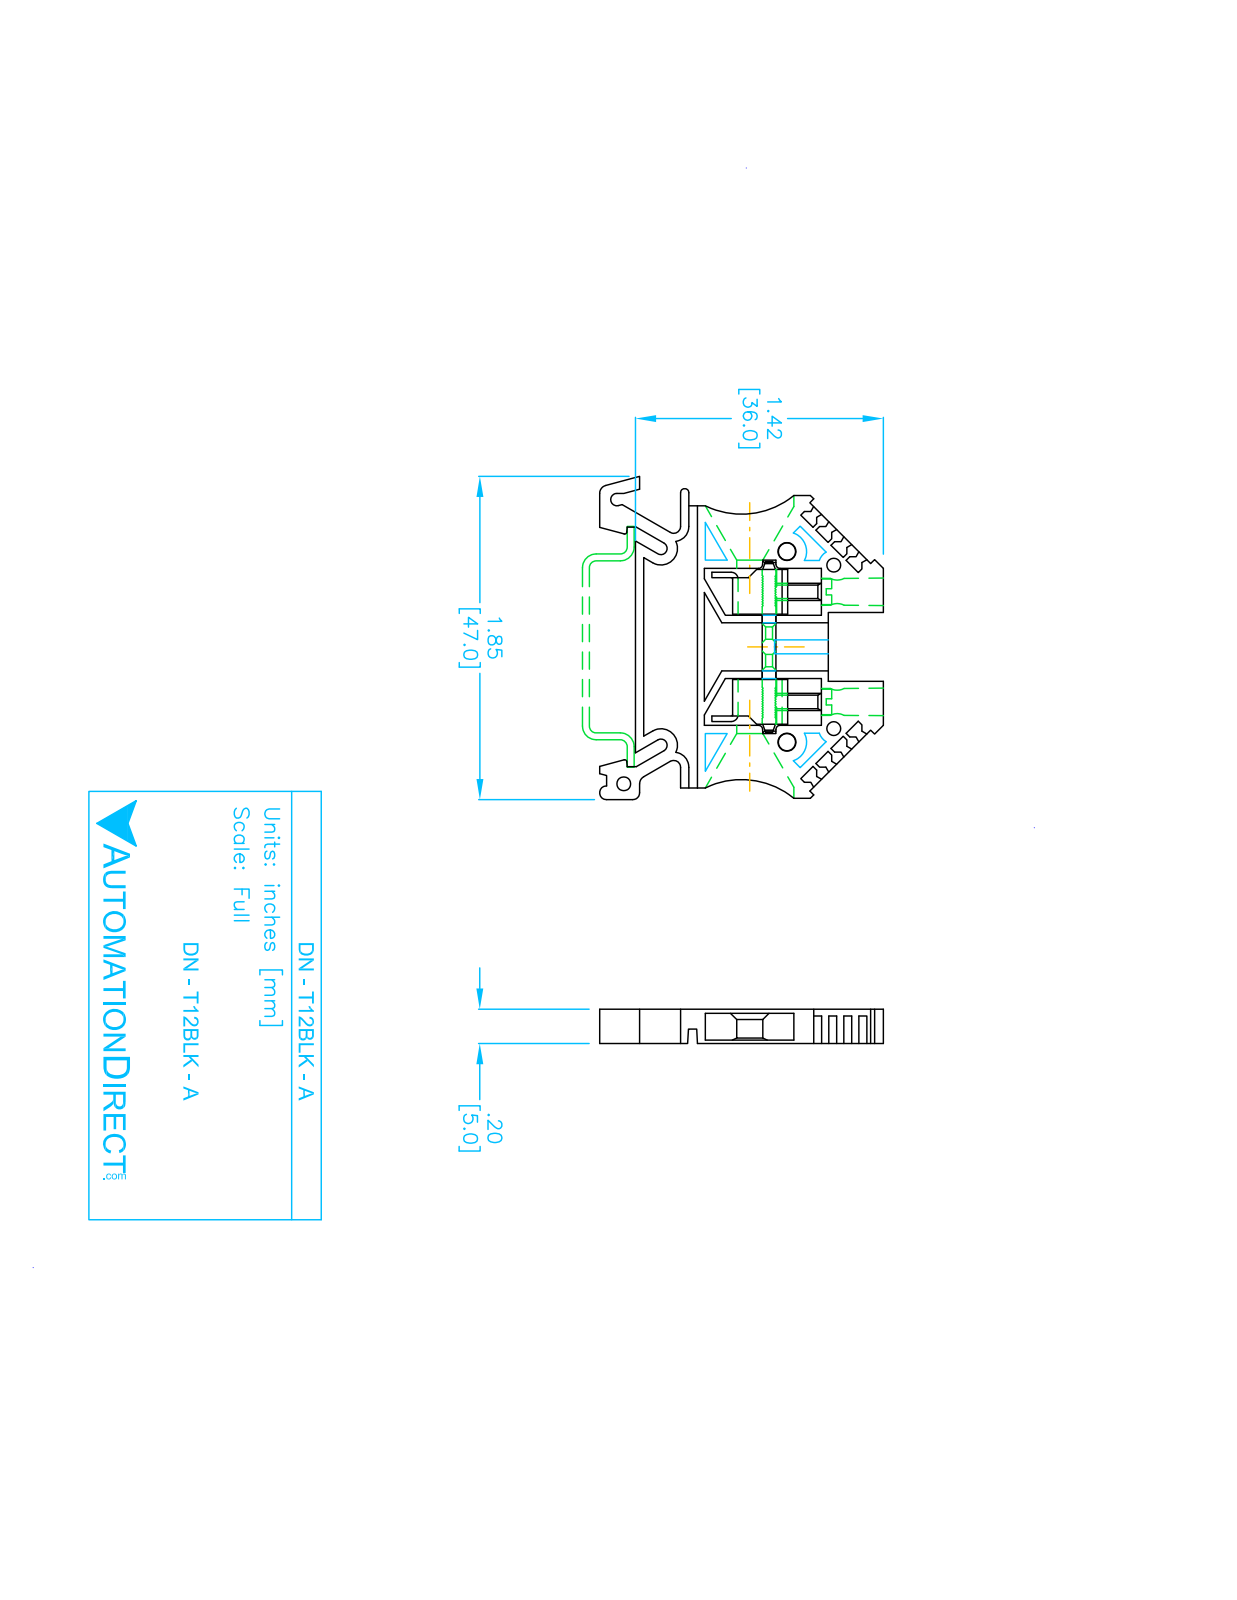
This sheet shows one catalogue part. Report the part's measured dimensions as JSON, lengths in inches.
{"part_name": "DN-T12BLK-A", "step_written_by": "SolidWorks 2017 (AUTOMOTIVE_DESIGN)", "units": "inches", "bodies": {"solids": 1, "faces": 169, "planar": 134, "cylindrical": 35, "other": 0}, "overall_size": [1.85, 1.622, 0.197], "volume_in3": 0.306, "surface_area_in2": 7.131, "round_holes": [[0.164, 2], [0.079, 1]], "partial_cylinders_radius": [[0.039, 4], [0.035, 3], [0.012, 2], [0.047, 2], [0.087, 2], [0.094, 2], [0.472, 2], [0.024, 1]], "face_to_face_distances": [0.189, 0.197, 0.087, 0.02, 0.106, 0.094, 0.114, 0.083, 0.102, 0.354], "hole_center_spacings": [0.589]}
